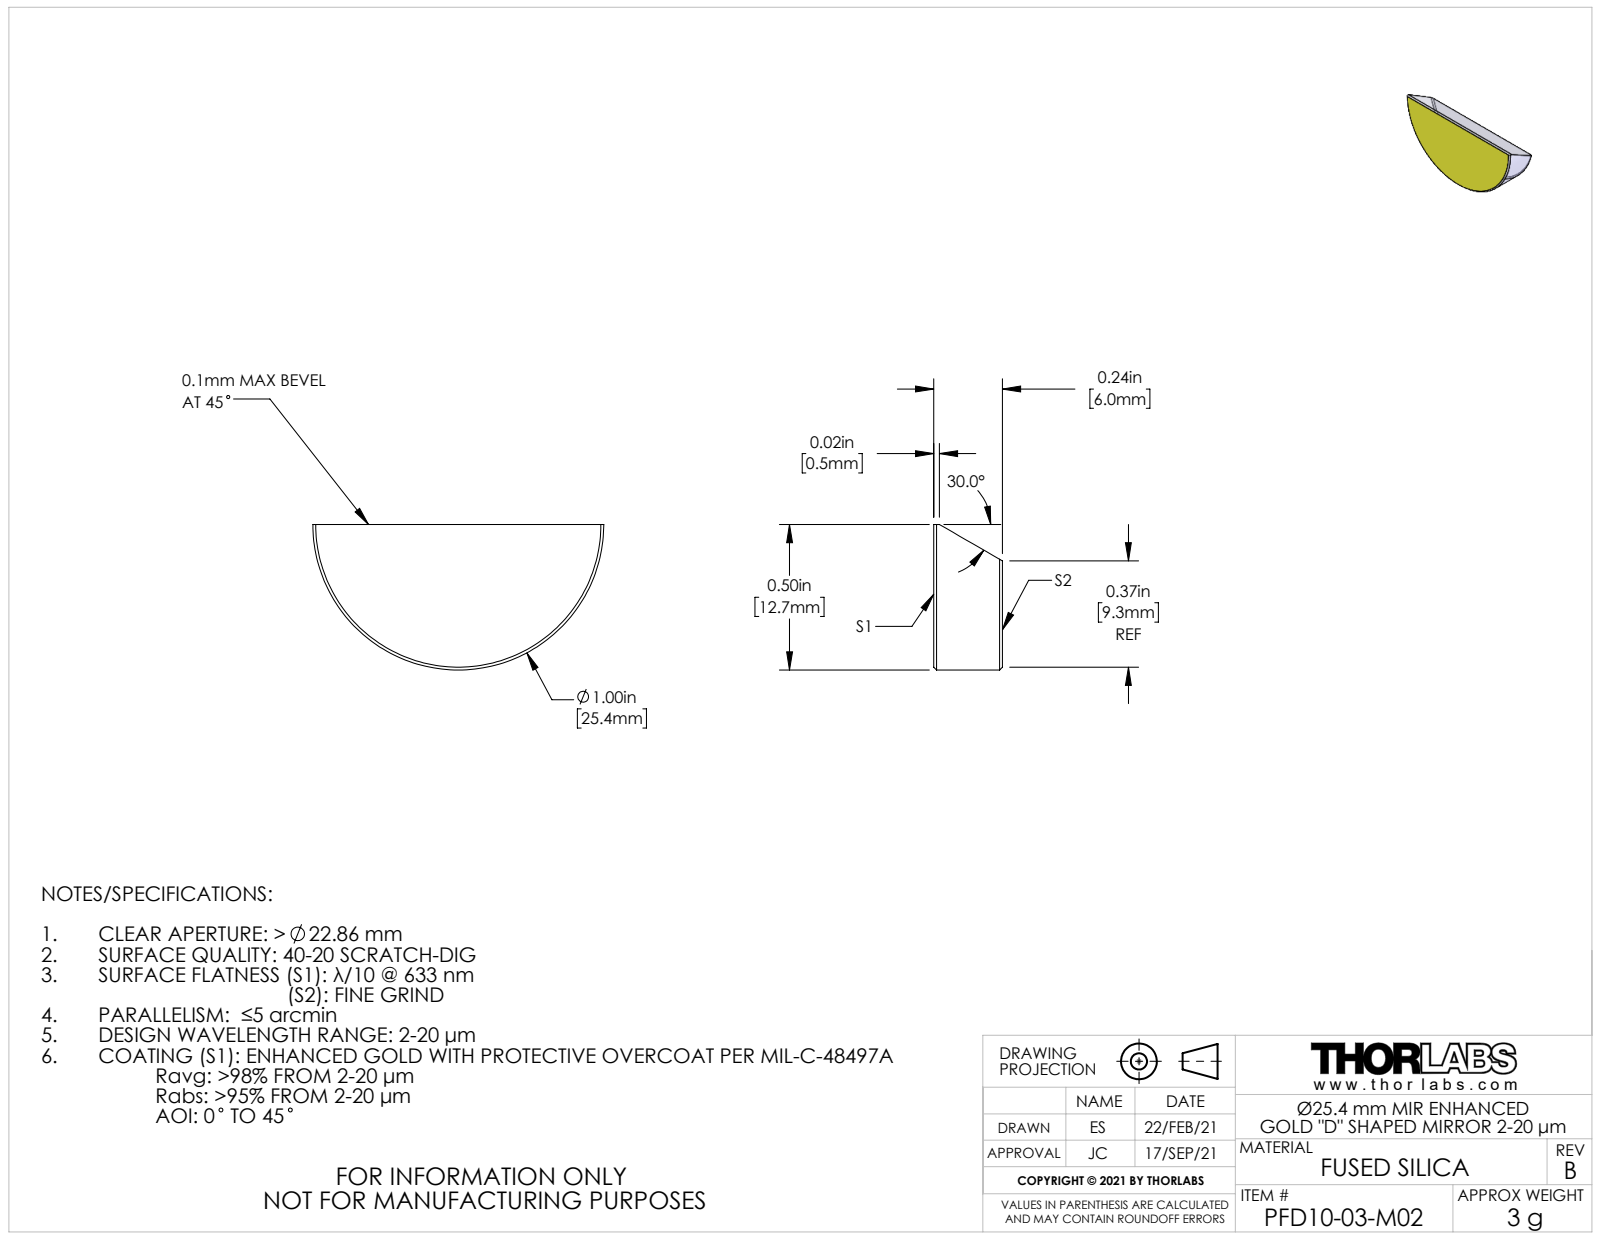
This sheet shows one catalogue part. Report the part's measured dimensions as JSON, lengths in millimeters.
{"part_name": "TTN227584-E0W", "step_written_by": "SolidWorks 2018 (CONFIG_CONTROL_DESIGN)", "units": "millimeters", "bodies": {"solids": 1, "faces": 7, "planar": 4, "cylindrical": 1, "other": 2}, "overall_size": [25.4, 12.7, 6], "volume_mm3": 1297, "surface_area_mm2": 810, "partial_cylinders_radius": [[12.7, 1]], "face_to_face_distances": [6]}
